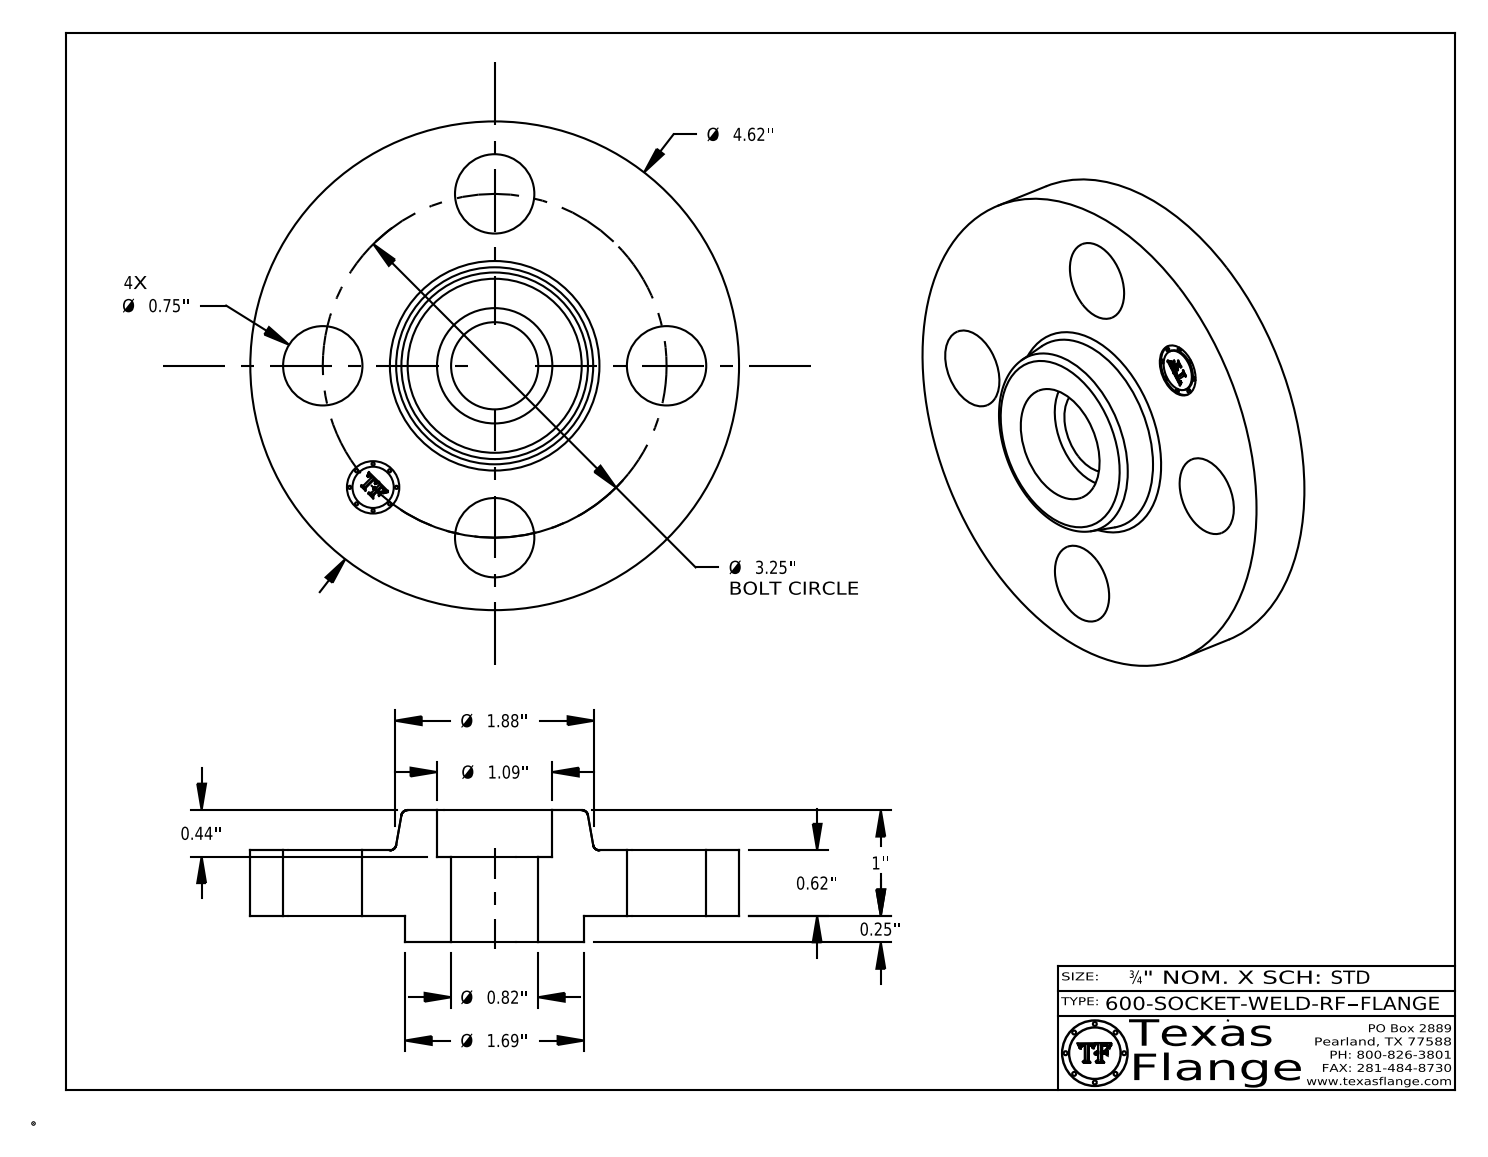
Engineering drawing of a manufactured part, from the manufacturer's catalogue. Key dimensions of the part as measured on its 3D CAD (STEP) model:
Part name (STEP PRODUCT): 600-SOCKET-WELD-RF
STEP written by: CATIA V5 STEP AP214 (AUTOMOTIVE_DESIGN)
Units: inches
Bodies: 1 solid, 412 faces (370 planar, 36 cylindrical, 6 other)
Overall size (bounding box): 4.62 × 4.62 × 1.25
Volume: 9.997 in³ · Surface area: 50.42 in²
Round holes (diameter × count): ⌀0.75 ×4, ⌀0.495 ×1, ⌀0.824 ×1, ⌀1.09 ×1
Round bosses / shafts (diameter × count): ⌀0.03 ×8, ⌀4.62 ×1, ⌀1.69 ×1, ⌀0.39 ×1
Main face-to-face distances: 0.62, 0.25, 0.87, 1.25, 1, 0.38, 0.81, 0.56, 0.06, 0.44
Hole centre spacings: 1.625, 2.298, 1.244, 3.003, 3.25
